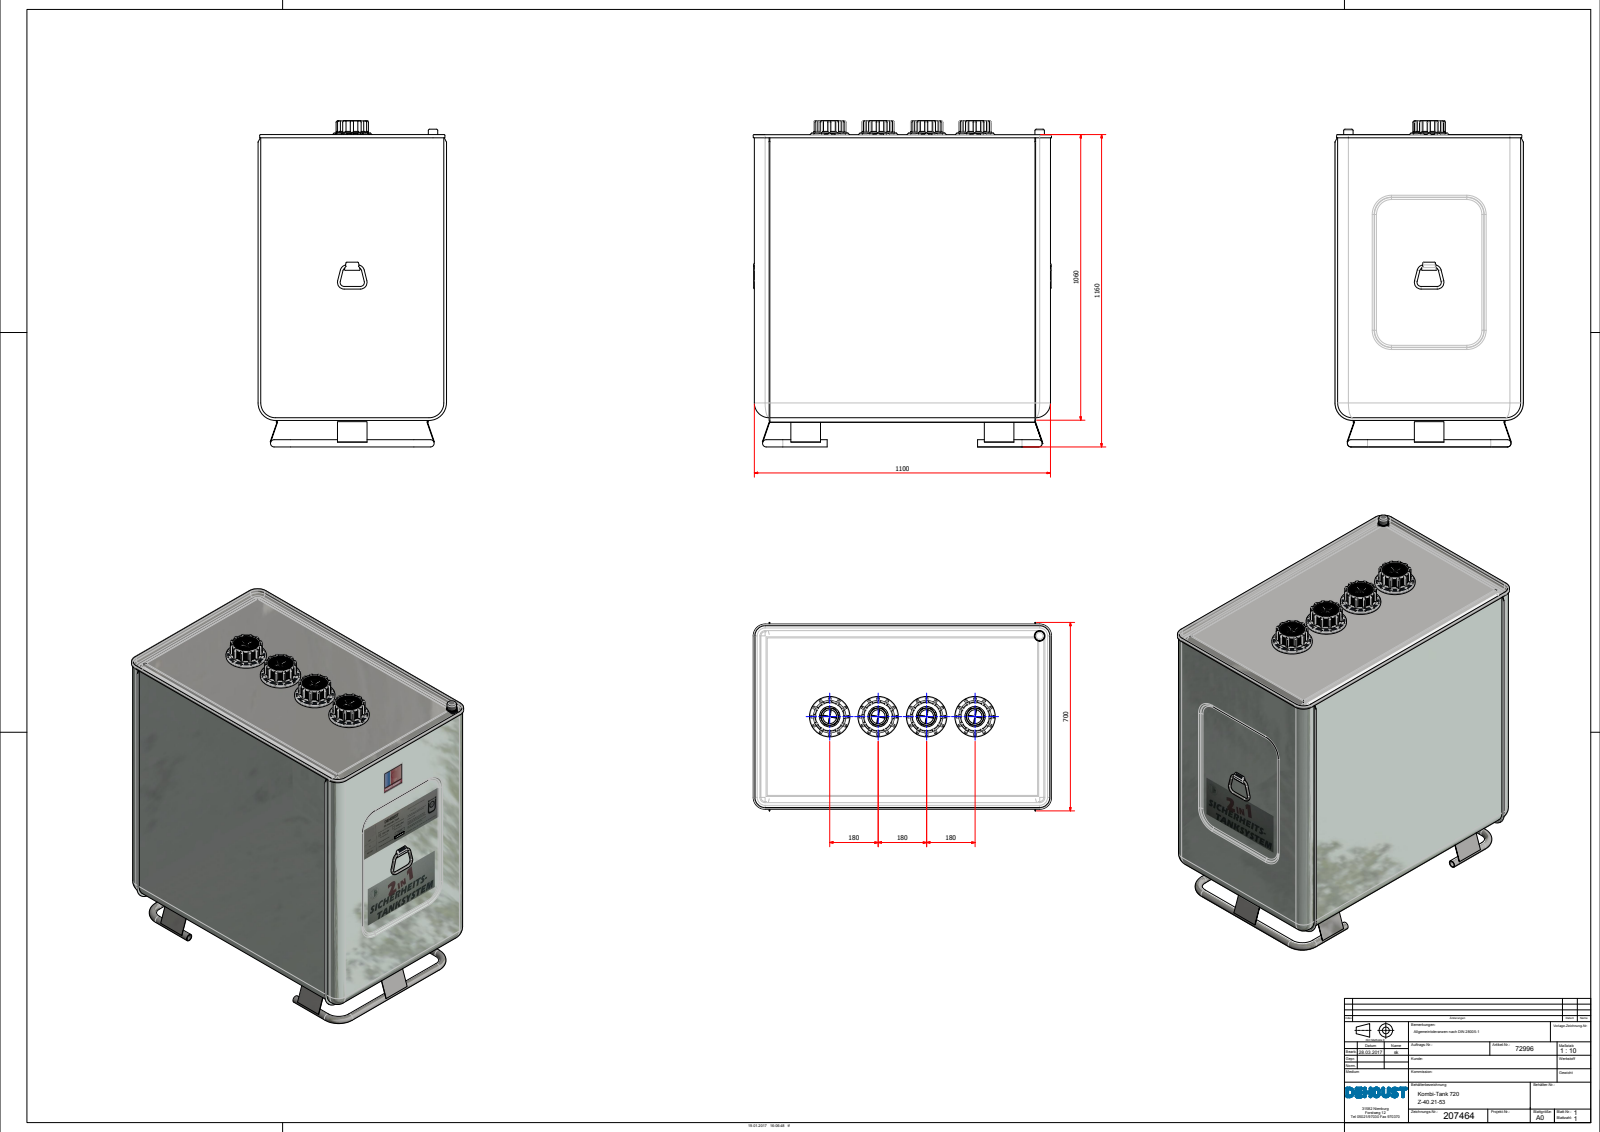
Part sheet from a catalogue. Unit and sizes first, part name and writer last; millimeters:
Units: millimetres
Overall size (bounding box): 1213.16 × 1108 × 700
Round holes (diameter × count): ⌀22.5 ×6, ⌀51.5 ×4, ⌀56.66 ×4, ⌀58 ×4, ⌀61 ×4, ⌀68 ×4, ⌀73 ×4, ⌀76 ×4, ⌀90 ×4, ⌀93 ×4, ⌀99.5 ×4, ⌀100 ×4
Round bosses / shafts (diameter × count): ⌀26.9 ×6, ⌀10 ×6, ⌀150 ×4, ⌀120 ×4, ⌀98 ×4, ⌀86.2 ×4, ⌀86 ×4, ⌀85 ×4
Partial cylindrical surfaces — rounded edges, fillets, slot ends (radius × count): R2 ×194, R1 ×146, R10 ×28, R1.5 ×24, R3 ×12, R8 ×12, R47 ×12, R1.25 ×8
Main face-to-face distances: 1, 3, 678, 2, 4, 5, 679, 677, 675, 674
Hole centre spacings: 581.04, 180, 360, 385.28, 517.13, 540, 671.72, 836.53
Volume: 23 080 000 mm³ · Surface area: 21 530 000 mm²
Bodies: 42 solids, 2282 faces (832 planar, 853 cylindrical, 597 other)
Part name (STEP PRODUCT): Kombi-Tank 720; Fuß_Kombi-Tank; Rahmen; Kantung Fußrahmen (+8 more)
STEP written by: Autodesk Inventor 2017 (AUTOMOTIVE_DESIGN)
